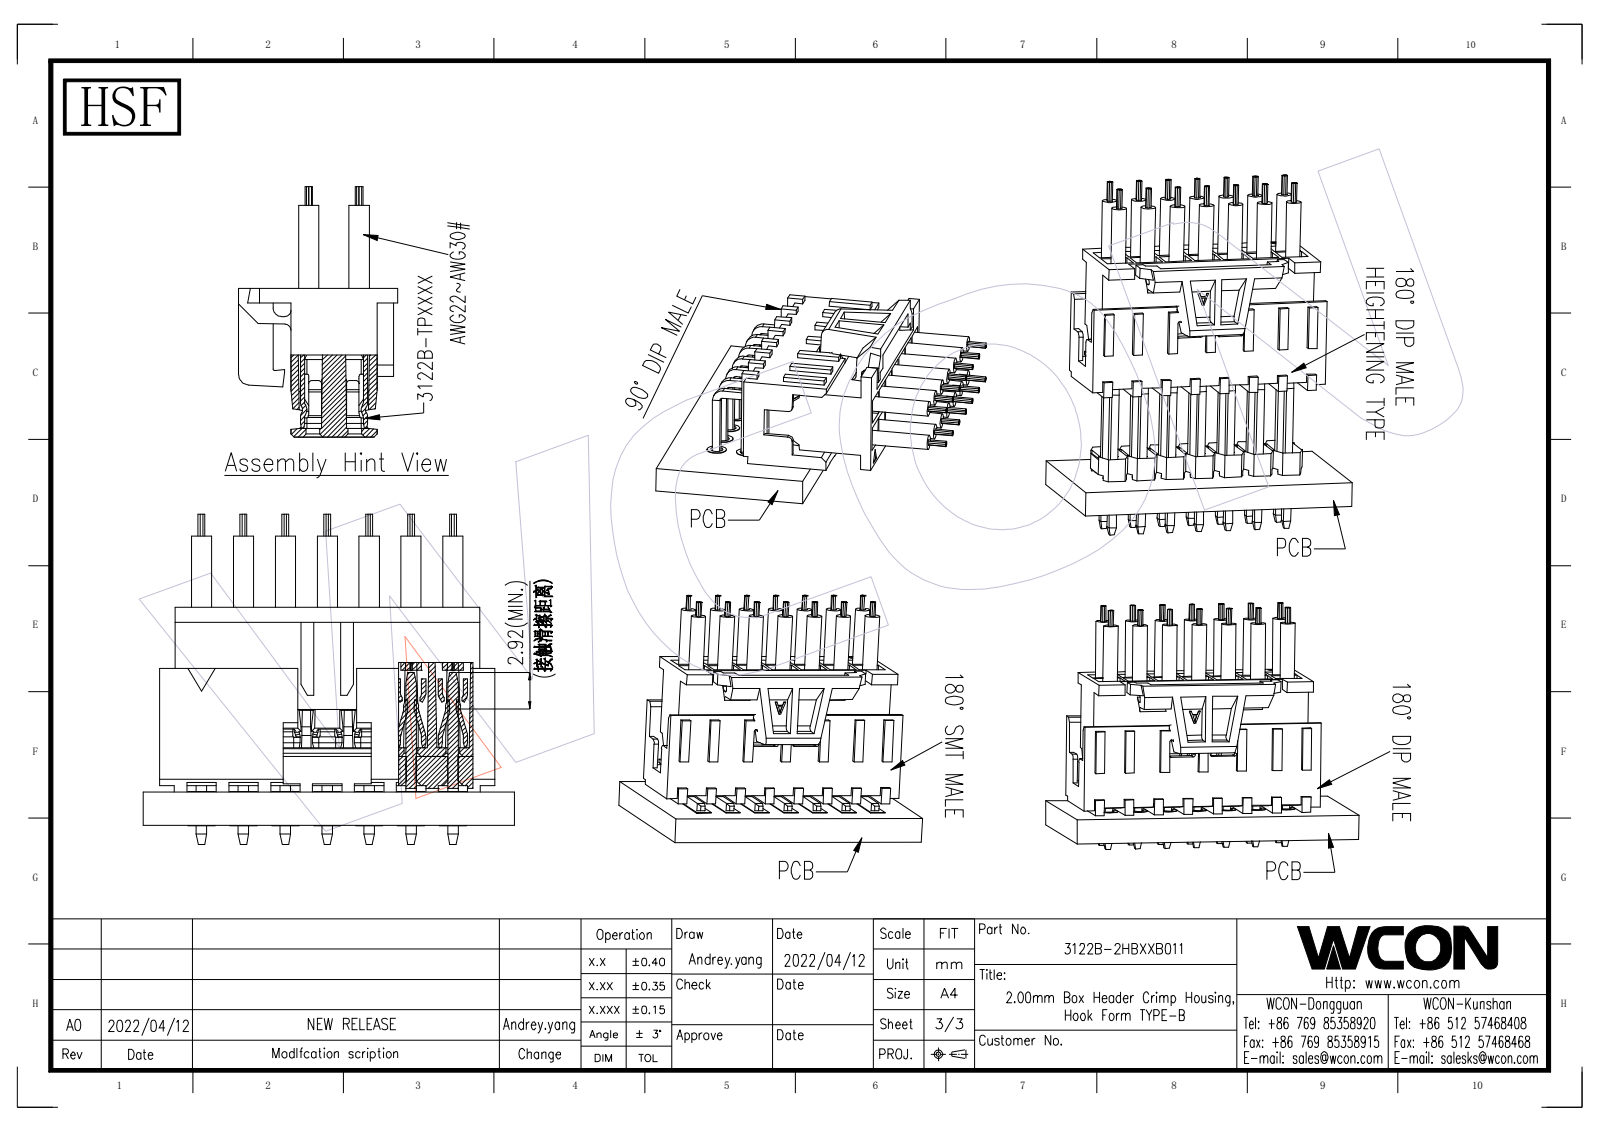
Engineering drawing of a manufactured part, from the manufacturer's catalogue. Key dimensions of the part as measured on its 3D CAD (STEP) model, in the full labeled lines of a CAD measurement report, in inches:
STEP written by: ZW3D to STEP translator (AUTOMOTIVE_DESIGN)
Units: inches
Bodies: 1 solid, 867 faces (846 planar, 11 cylindrical, 10 other)
Overall size (bounding box): 0.809 × 0.299 × 0.28
Volume: 0.033 in³ · Surface area: 1.682 in²
Partial cylindrical surfaces — rounded edges, fillets, slot ends (radius × count): R0.012 ×3, R0.016 ×1, R0.02 ×1
Main face-to-face distances: 0.236, 0.079, 0.157, 0.161, 0.315, 0.28, 0.394, 0.267, 0.013, 0.472
